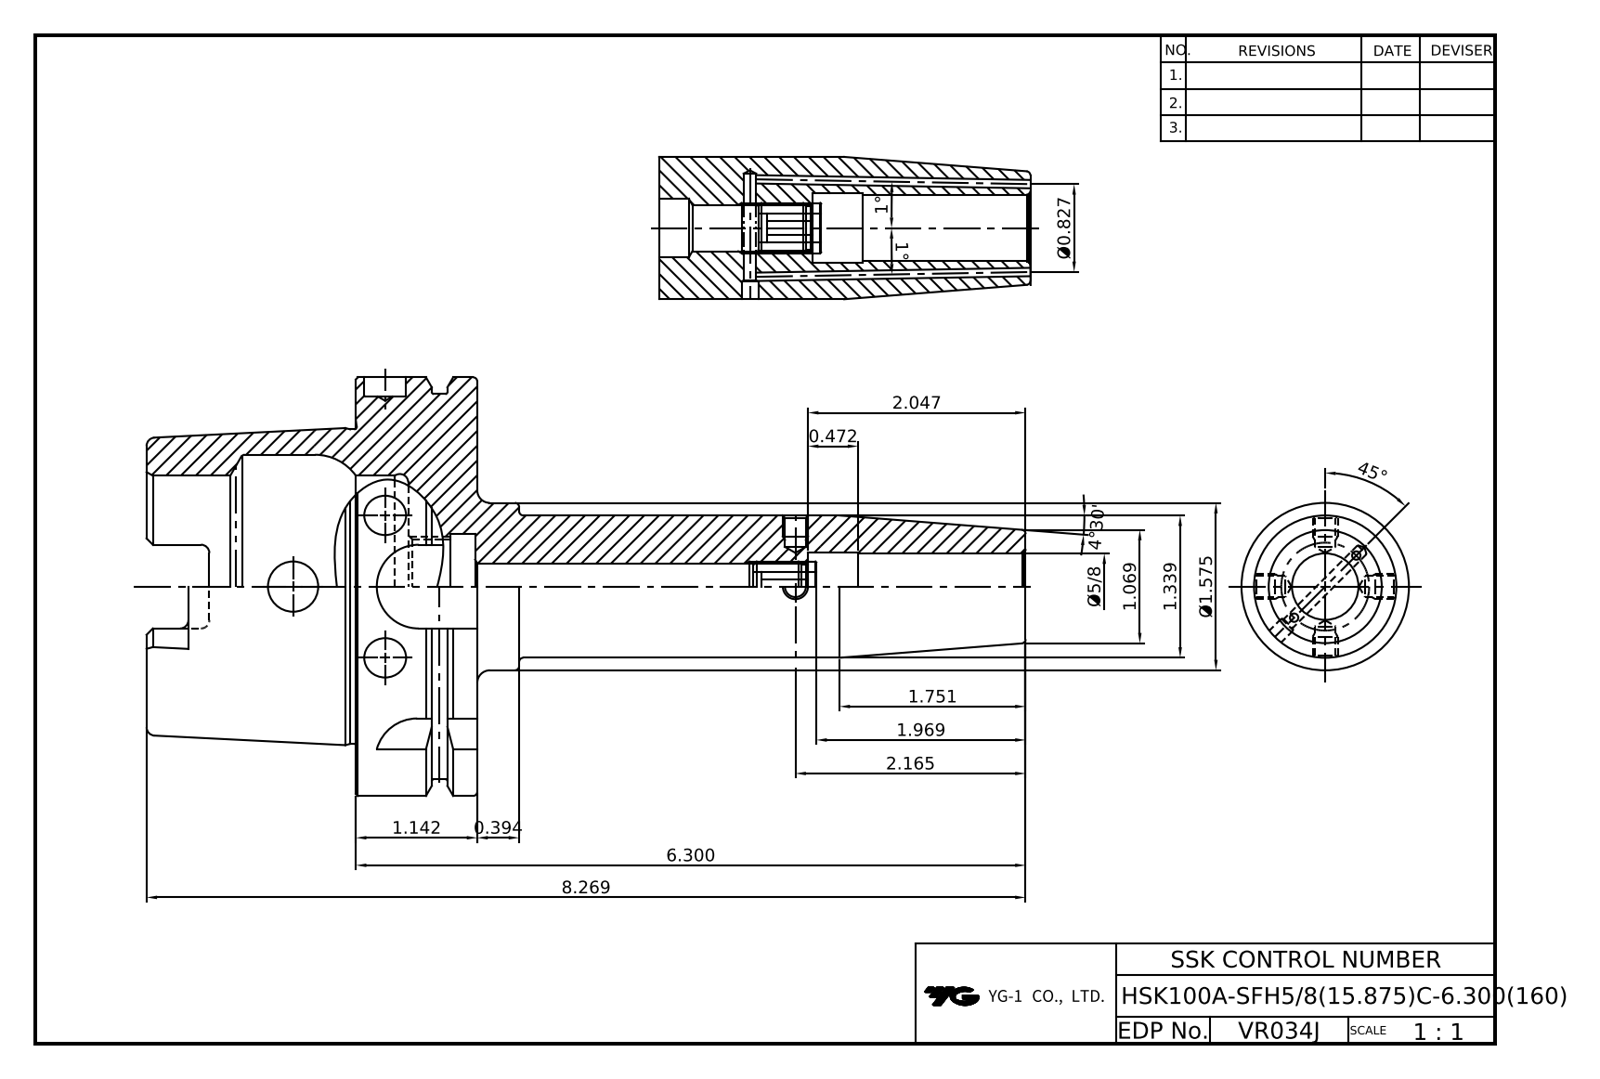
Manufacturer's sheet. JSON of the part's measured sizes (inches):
{"part_name": "LO-HSK100A-SFH15.875C-160", "step_written_by": "Autodesk Inventor 2022 (AUTOMOTIVE_DESIGN)", "units": "inches", "bodies": {"solids": 1, "faces": 121, "planar": 39, "cylindrical": 37, "other": 45}, "overall_size": [8.268, 3.937, 3.937], "volume_in3": 21.39, "surface_area_in2": 106.7, "round_holes": [[0.079, 2], [0.394, 1], [0.43, 1], [0.472, 1], [0.625, 1], [0.672, 1], [0.881, 1], [0.984, 1], [2.087, 1], [2.48, 1]], "round_bosses_or_shafts": [[3.937, 1], [3.622, 1], [2.969, 1], [1.575, 1], [1.339, 1]], "partial_cylinders_radius": [[0.079, 6], [0.192, 4], [0.394, 4]], "face_to_face_distances": [1.142, 0.492, 0.65, 3.11, 2.461, 1.969, 3.465, 3.091, 1.122, 0.63]}
